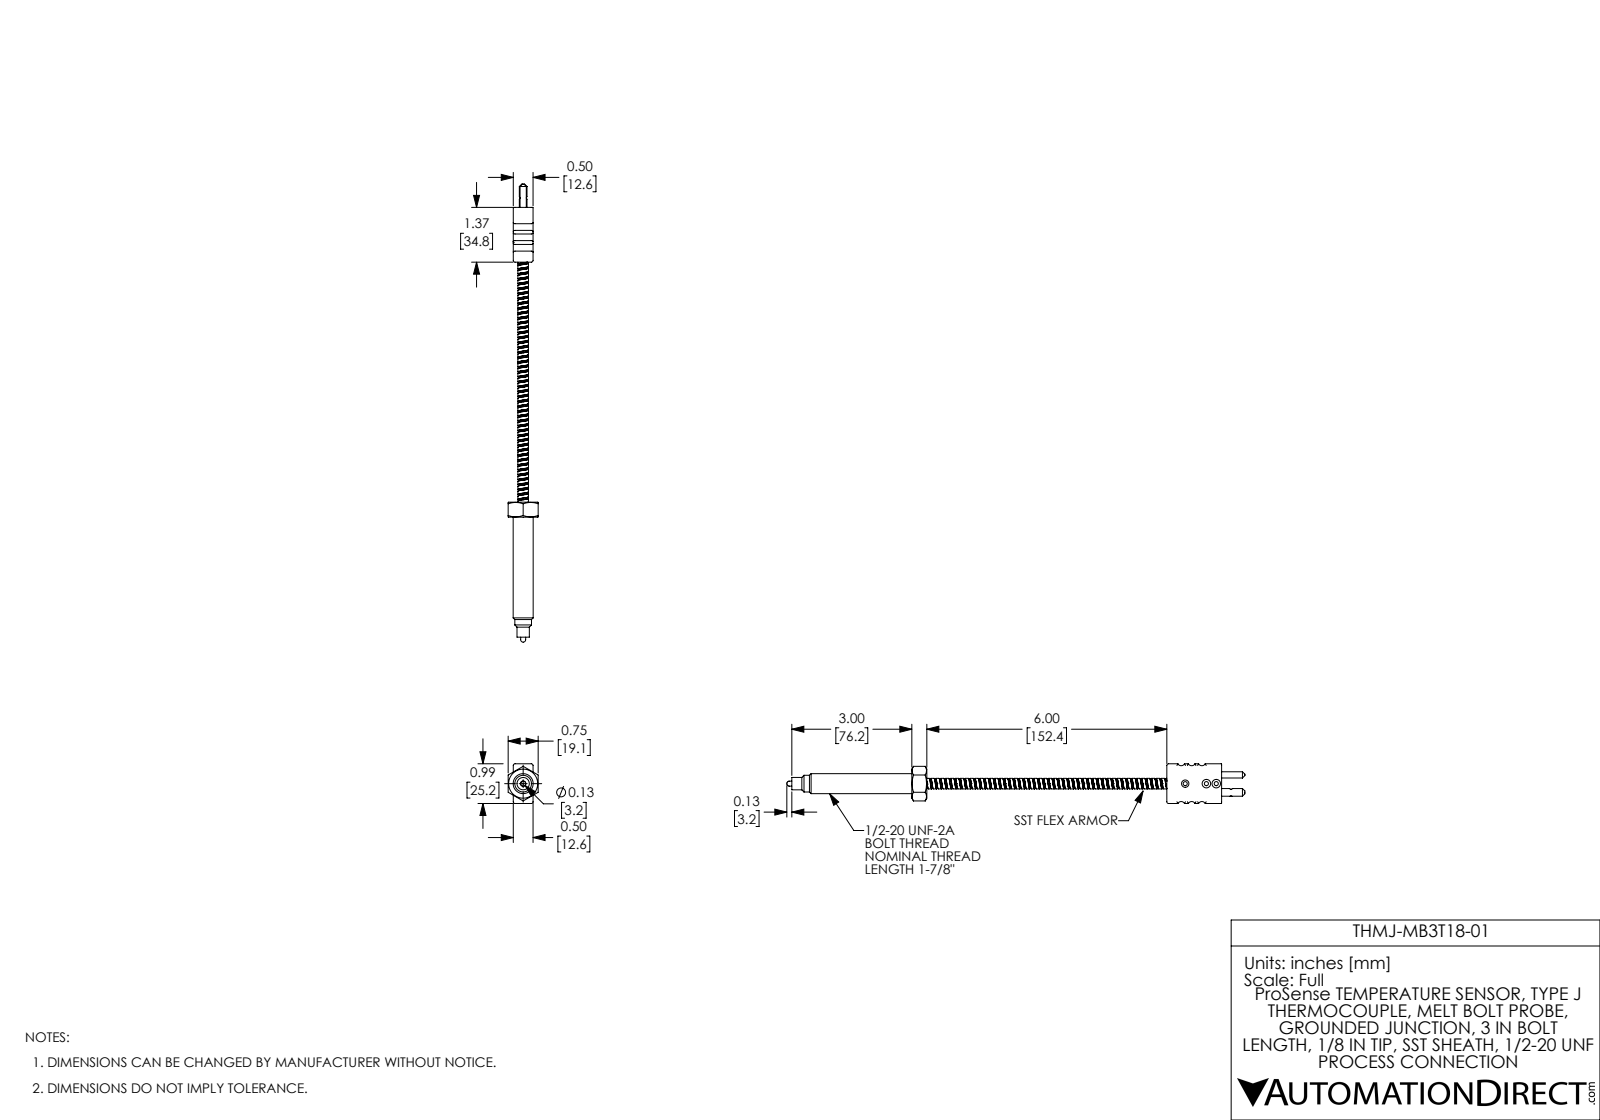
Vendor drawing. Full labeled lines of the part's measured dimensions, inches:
Part name (STEP PRODUCT): THMJ-MB3T18-01
STEP written by: SolidWorks 2017 (AUTOMOTIVE_DESIGN)
Units: inches
Bodies: 3 solids, 312 faces (69 planar, 172 cylindrical, 71 other)
Overall size (bounding box): 11.451 × 0.993 × 0.75
Volume: 1.684 in³ · Surface area: 19.16 in²
Round holes (diameter × count): ⌀0.103 ×2, ⌀0.158 ×2, ⌀0.135 ×1, ⌀0.185 ×1, ⌀0.294 ×1, ⌀0.308 ×1
Round bosses / shafts (diameter × count): ⌀0.5 ×1, ⌀0.417 ×1, ⌀0.309 ×1, ⌀0.278 ×1, ⌀0.265 ×1, ⌀0.191 ×1, ⌀0.156 ×1, ⌀0.125 ×1
Partial cylindrical surfaces — rounded edges, fillets, slot ends (radius × count): R0.045 ×8, R0.095 ×6, R0.01 ×4
Main face-to-face distances: 0.495, 0.75, 7.369, 0.993, 0.127, 0.622, 1.369, 6, 7.744, 6.375
Hole centre spacings: 0.217, 0.328, 0.572, 0.247, 0.433, 0.529, 0.776
